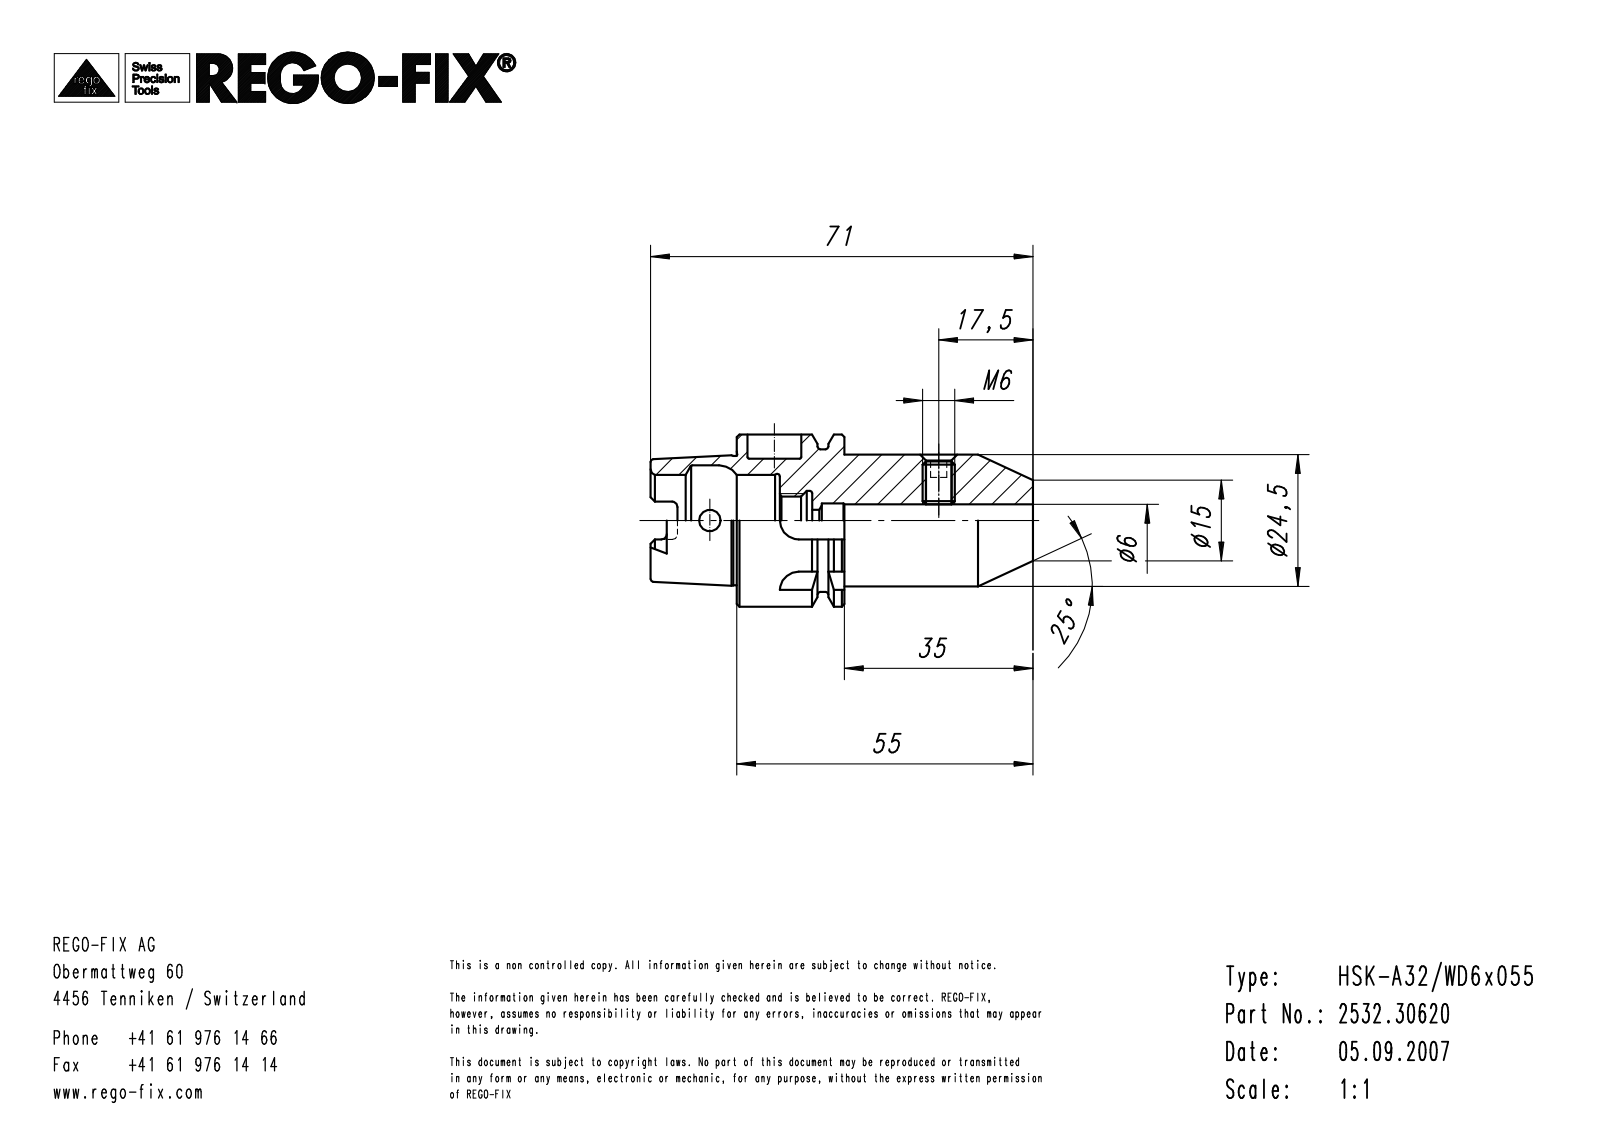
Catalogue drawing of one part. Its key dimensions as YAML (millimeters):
step_written_by: "Unknown (AUTOMOTIVE_DESIGN)"
units: millimeters
bodies: {solids: 1, faces: 129, planar: 47, cylindrical: 35, other: 47}
overall_size: [71, 32, 32]
volume: 27652
surface_area: 9993
round_holes:
  - {diameter: 10, count: 2}
  - {diameter: 4, count: 1}
  - {diameter: 4.2, count: 1}
  - {diameter: 4.92, count: 1}
  - {diameter: 6, count: 1}
  - {diameter: 6.4, count: 1}
  - {diameter: 8.92, count: 1}
  - {diameter: 11, count: 1}
  - {diameter: 17, count: 1}
  - {diameter: 20.5, count: 1}
round_bosses_or_shafts:
  - {diameter: 32, count: 1}
  - {diameter: 26.5, count: 1}
  - {diameter: 24.5, count: 1}
  - {diameter: 24.13, count: 1}
partial_cylinders:
  - {radius: 1, count: 6}
  - {radius: 1.38, count: 4}
  - {radius: 3.5, count: 4}
face_to_face_distances: [20, 8, 6, 12, 55, 47, 35, 26, 3, 5]
hole_center_spacings: [30.5]
